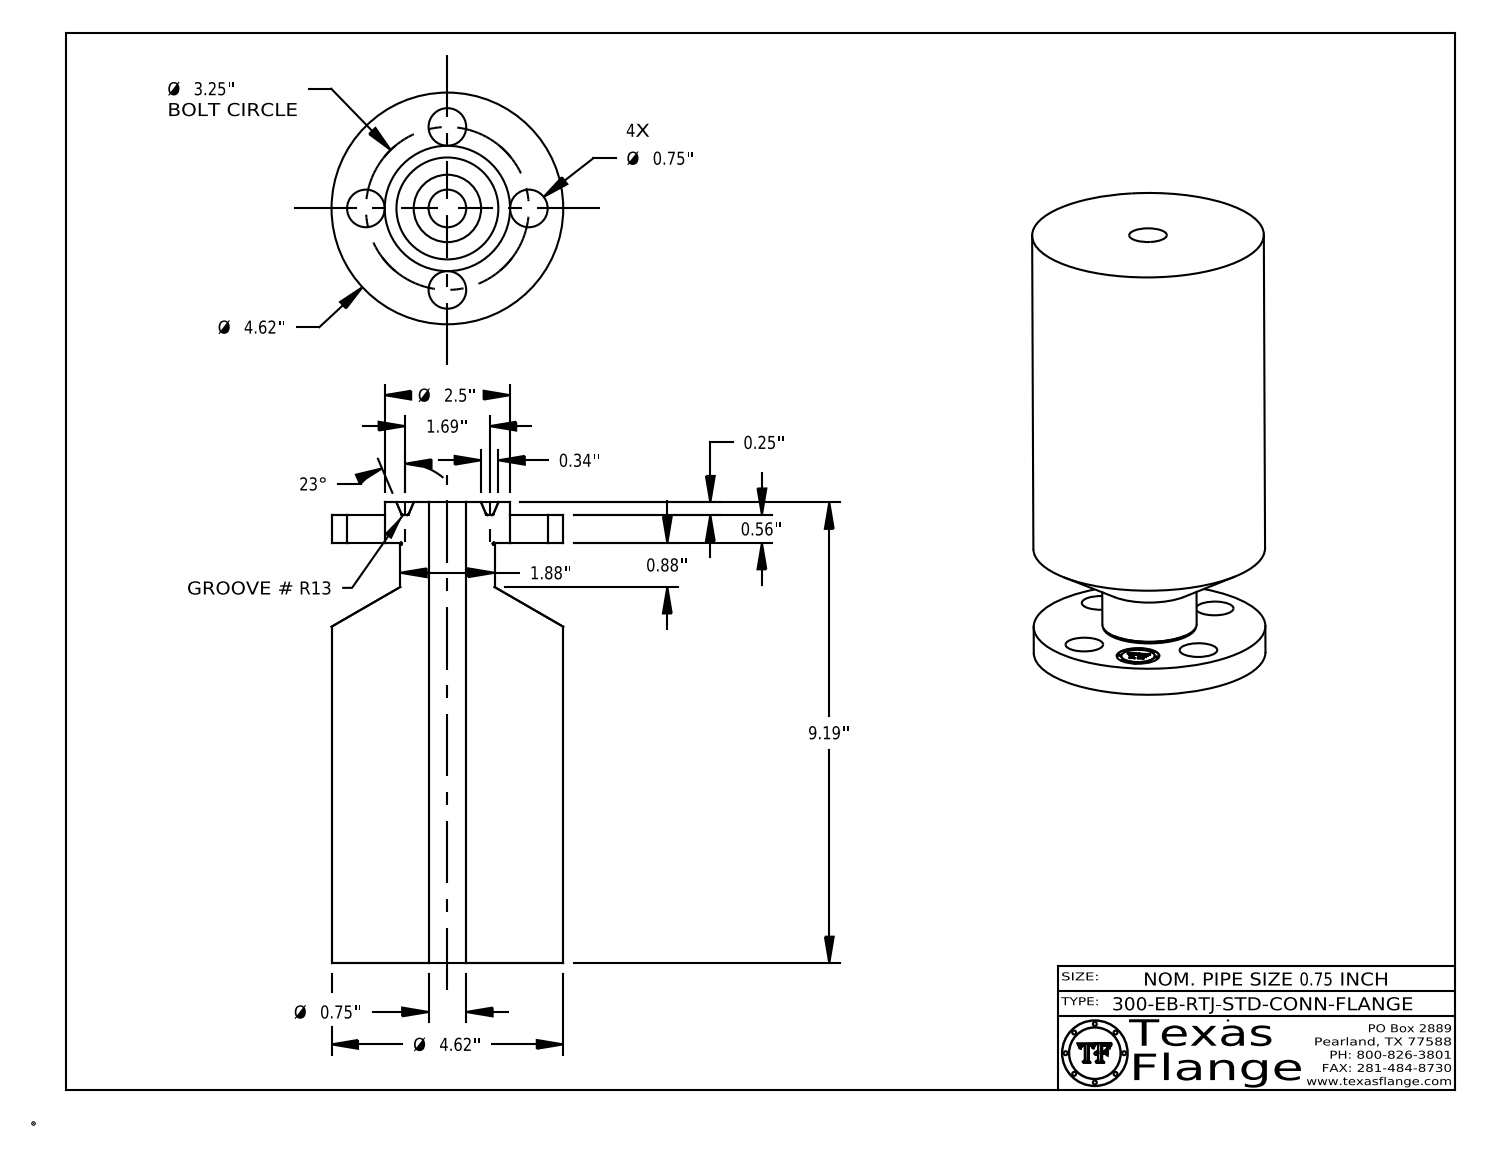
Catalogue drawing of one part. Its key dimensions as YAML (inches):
part_name: "0.75-300-EB-RTJ-STD-CONN-FLANGE"
step_written_by: "CATIA V5 STEP AP214 (AUTOMOTIVE_DESIGN)"
units: inches
bodies: {solids: 1, faces: 423, planar: 371, cylindrical: 38, other: 14}
overall_size: [9.188, 4.62, 4.62]
volume: 127.1
surface_area: 200.8
round_holes:
  - {diameter: 0.75, count: 5}
  - {diameter: 0.85, count: 1}
round_bosses_or_shafts:
  - {diameter: 0.051, count: 8}
  - {diameter: 4.62, count: 1}
  - {diameter: 2.5, count: 1}
  - {diameter: 1.88, count: 1}
  - {diameter: 0.67, count: 1}
face_to_face_distances: [8.38, 0.557, 8.937, 0.25, 0.807, 9.187, 0.802, 0.552, 8.385, 0.254]
hole_center_spacings: [1.625, 2.298, 1.244, 3.003, 3.25]
